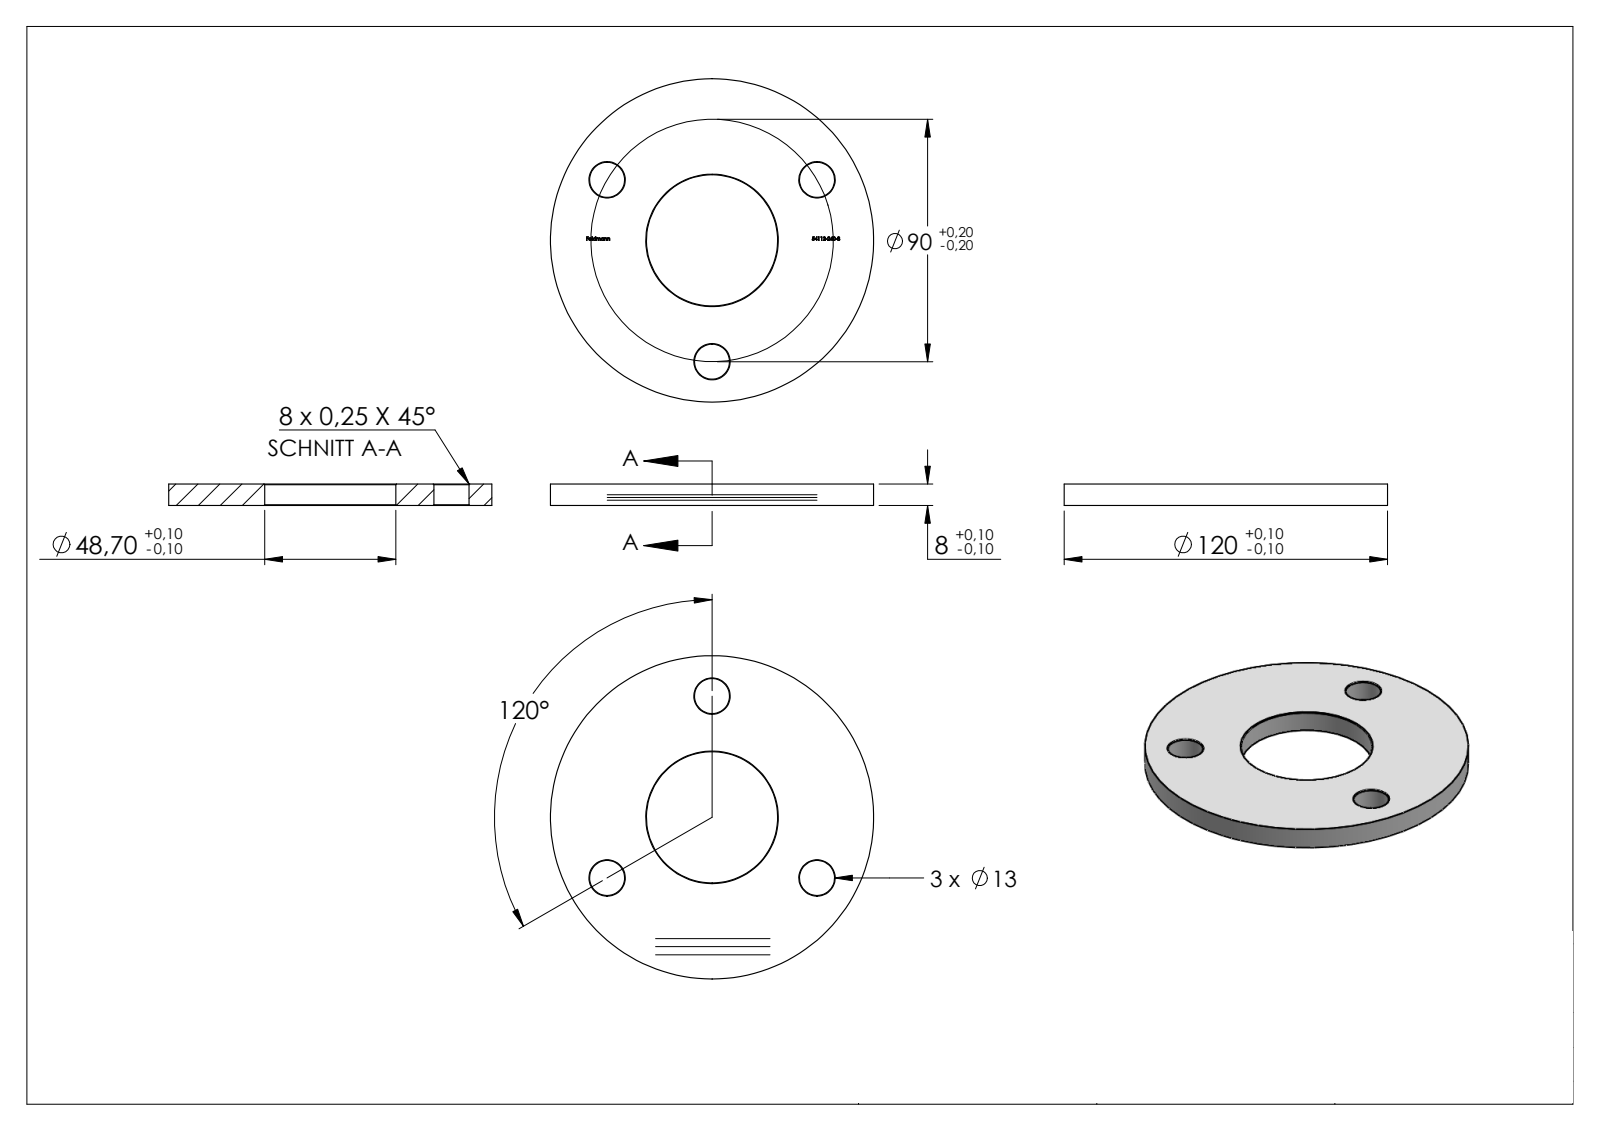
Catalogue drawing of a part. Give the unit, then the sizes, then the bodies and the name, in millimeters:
Units: millimetres
Overall size (bounding box): 120 × 120 × 8
Round holes (diameter × count): ⌀13 ×3, ⌀48.7 ×1
Round bosses / shafts (diameter × count): ⌀120 ×1
Main face-to-face distances: 8, 7.9, 0.44, 0.88, 1.02, 1.19, 86.18, 87.2, 1.32, 0.58
Hole centre spacings: 45, 77.94
Volume: 72 373 mm³ · Surface area: 23 248 mm²
Bodies: 1 solid, 267 faces (147 planar, 10 cylindrical, 110 other)
Part name (STEP PRODUCT): 54112-240-8
STEP written by: SolidWorks 2018 (CONFIG_CONTROL_DESIGN)
